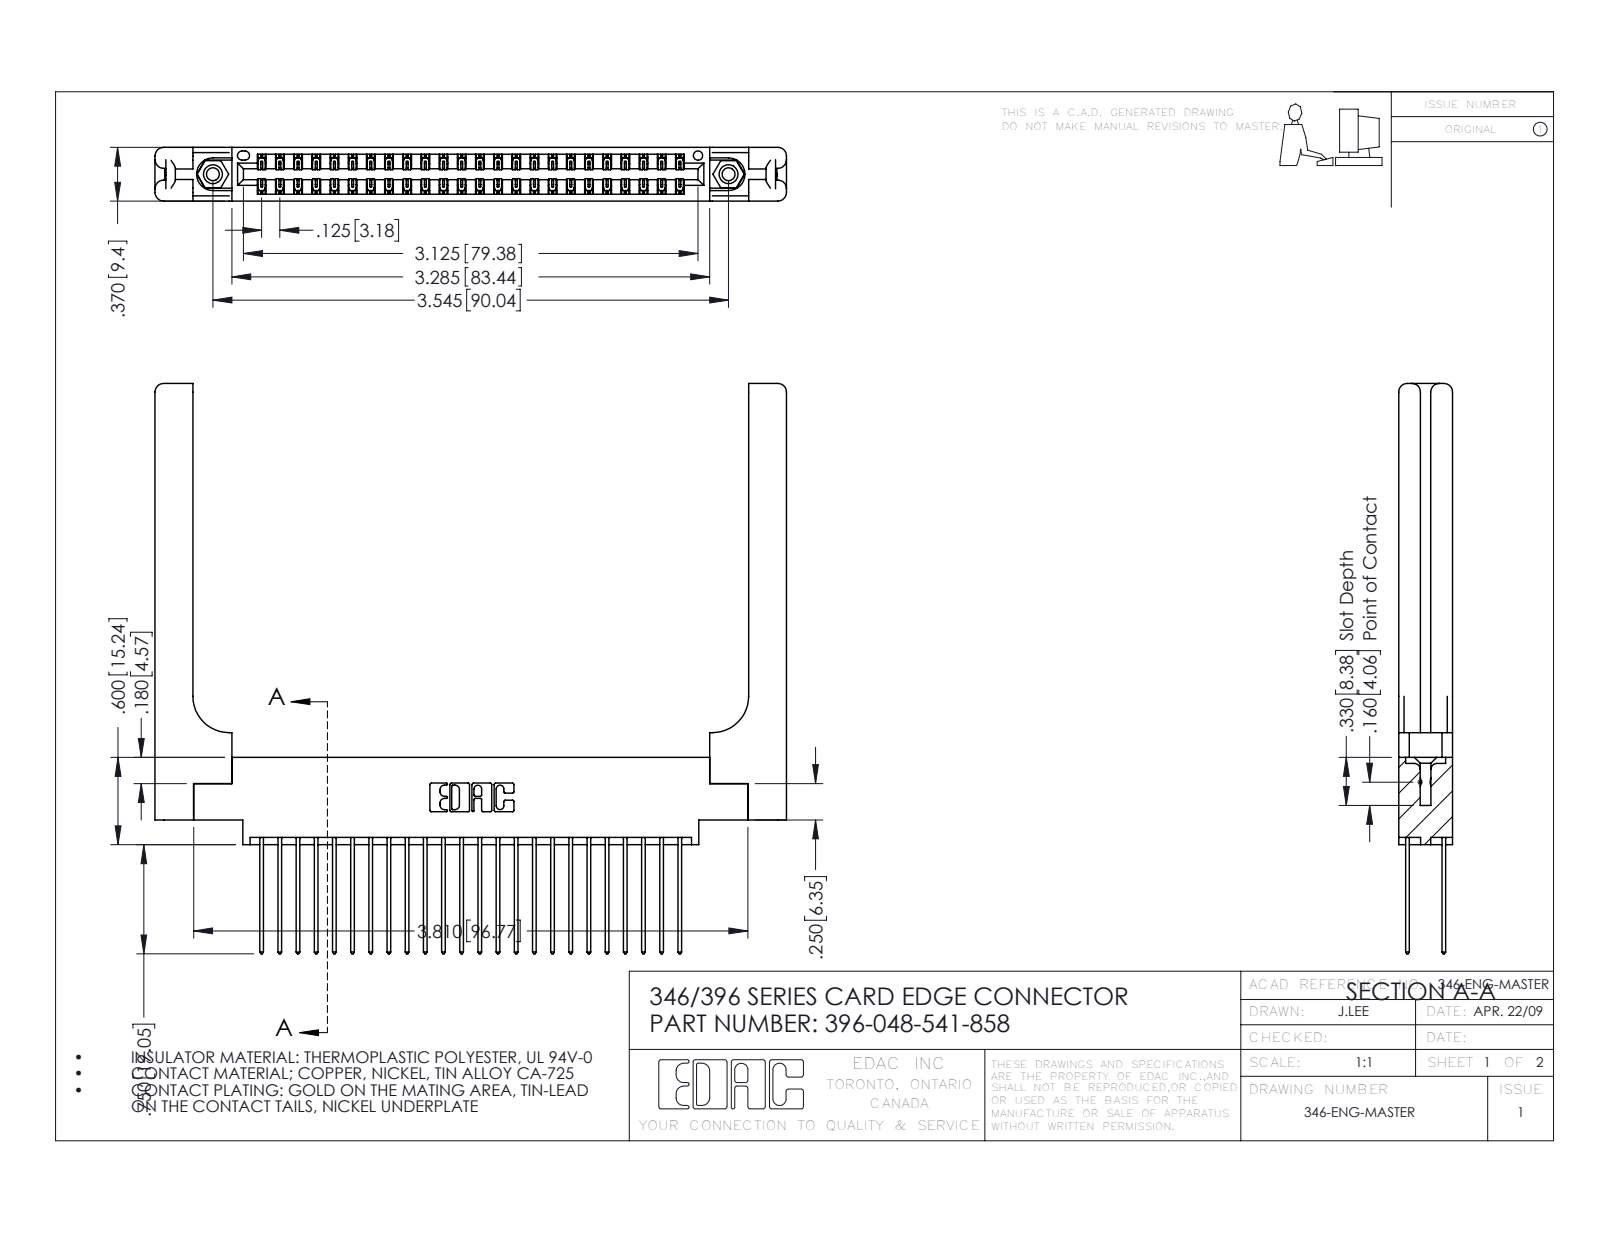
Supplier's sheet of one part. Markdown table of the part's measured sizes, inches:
| quantity | value |
| --- | --- |
| part name | 345-250-001_345-250-001-102; 346-220-058_345-220-058; 346 Part_0.170 Offset - 0.156 Dia-TH; 345-292-001_345-293-141 (+1 more) |
| STEP written by | SolidWorks 2016 (CONFIG_CONTROL_DESIGN) |
| units | inches |
| bodies | 53 solids, 2878 faces (1908 planar, 910 cylindrical, 60 other) |
| overall size | 4.341 × 3.92 × 0.37 |
| volume | 1.112 in³ |
| surface area | 32.46 in² |
| round holes (diameter × count) | 0.089 × 2, 0.125 × 2, 0.156 × 2, 0.064 × 1 |
| round bosses / shafts (diameter × count) | 0.155 × 2 |
| partial cylindrical surfaces (radius × count) | 0.006 × 72, 0.01 × 48, 0.01 × 22, 0.06 × 16, 0.007 × 6, 0.031 × 6, 0.026 × 3, 0.014 × 2 |
| main face-to-face distances | 0.37, 0.072, 0.048, 0.322, 0.25, 0.025, 0.298, 0.148, 0.15, 0.275 |
| hole center spacings | 0.246, 3.337, 3.545 |
